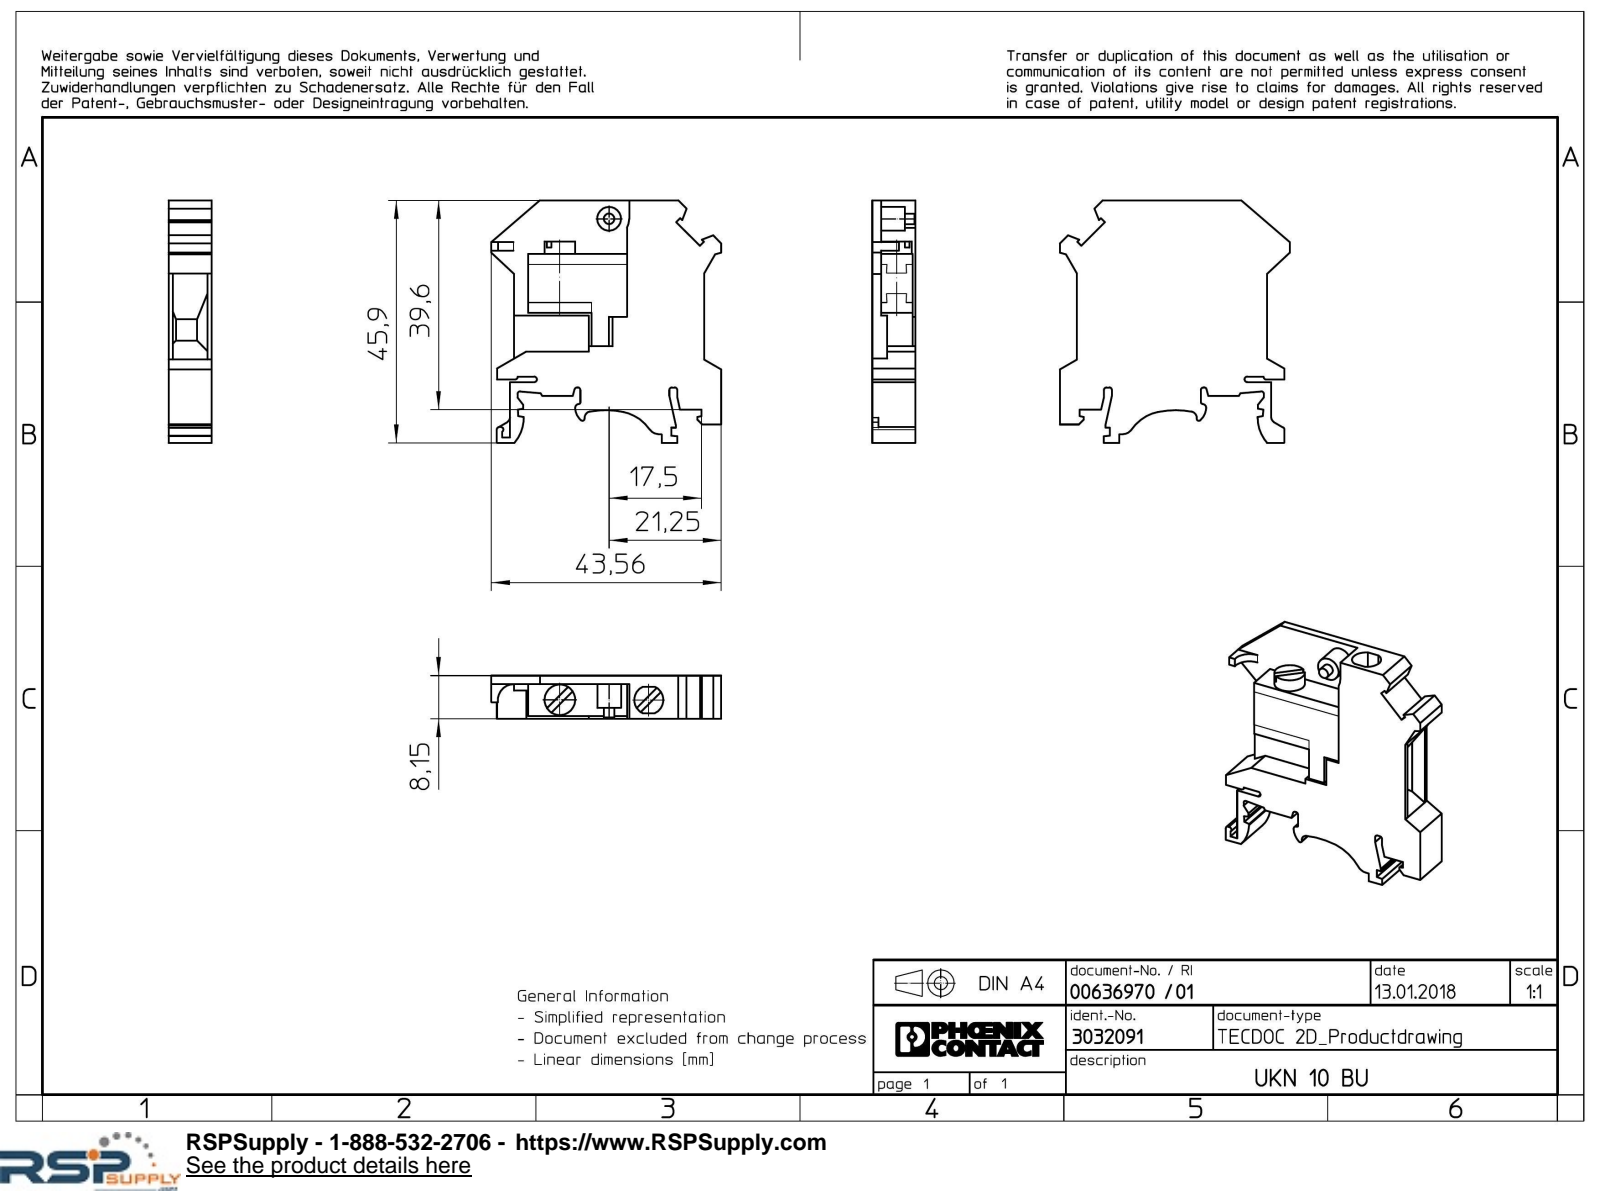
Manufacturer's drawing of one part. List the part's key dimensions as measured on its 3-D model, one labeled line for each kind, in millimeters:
Part name (STEP PRODUCT): UKN_10_BU-select
STEP written by: Creo Elements/Direct Modeling 18.1I 14-Aug-2016 (C) Parametric Technology GmbH (AUTOMOTIVE_DESIGN)
Units: millimetres
Bodies: 1 solid, 150 faces (120 planar, 30 cylindrical, 0 other)
Overall size (bounding box): 45.9 × 43.56 × 8.15
Volume: 9 155 mm³ · Surface area: 5 739 mm²
Round bosses / shafts (diameter × count): ⌀5.8 ×1, ⌀4.5 ×1, ⌀2 ×1
Partial cylindrical surfaces — rounded edges, fillets, slot ends (radius × count): R0.5 ×8, R0.3 ×1, R0.4 ×1, R0.52 ×1, R0.53 ×1, R0.7 ×1, R1 ×1, R1.2 ×1
Main face-to-face distances: 8.15, 0.5, 1.65, 6.5, 6, 7.65, 7.35, 1.2, 5.3, 2.85
